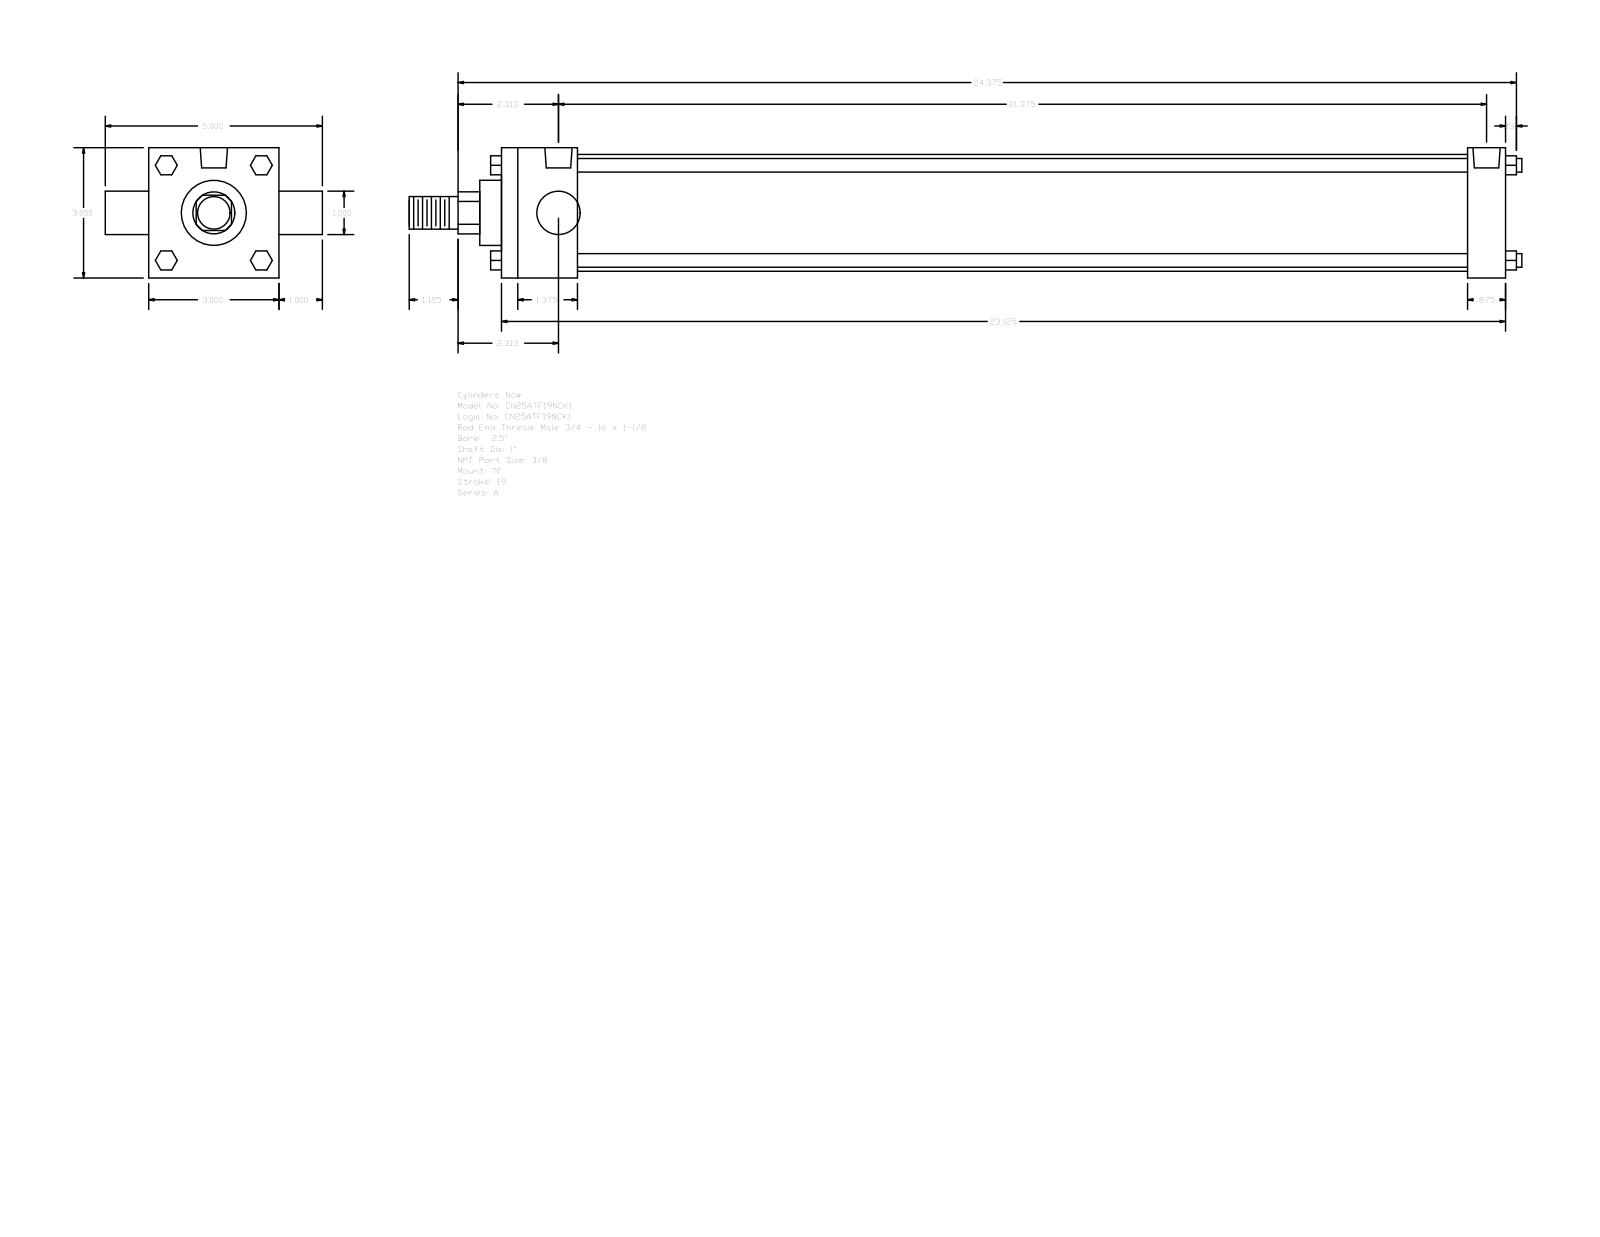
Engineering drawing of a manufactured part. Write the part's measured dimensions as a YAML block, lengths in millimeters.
part_name: "A_TF__0250_1"
step_written_by: "GSSL Pune (CONFIG_CONTROL_DESIGN)"
units: millimeters
bodies: {solids: 0, faces: 120, planar: 92, cylindrical: 28, other: 0}
overall_size: [650.88, 127, 76.2]
round_holes:
  - {diameter: 5.56, count: 3}
  - {diameter: 15.93, count: 2}
round_bosses_or_shafts:
  - {diameter: 7.94, count: 4}
  - {diameter: 25.4, count: 2}
  - {diameter: 68.33, count: 1}
  - {diameter: 38.1, count: 1}
  - {diameter: 19.05, count: 1}
partial_cylinders:
  - {radius: 12.29, count: 1}
face_to_face_distances: [76.2, 587.37, 44.45, 565.15, 520.7, 542.92, 22.22, 25.4, 101.6, 600.07]
hole_center_spacings: [2.38, 545.3, 542.92, 547.68]
